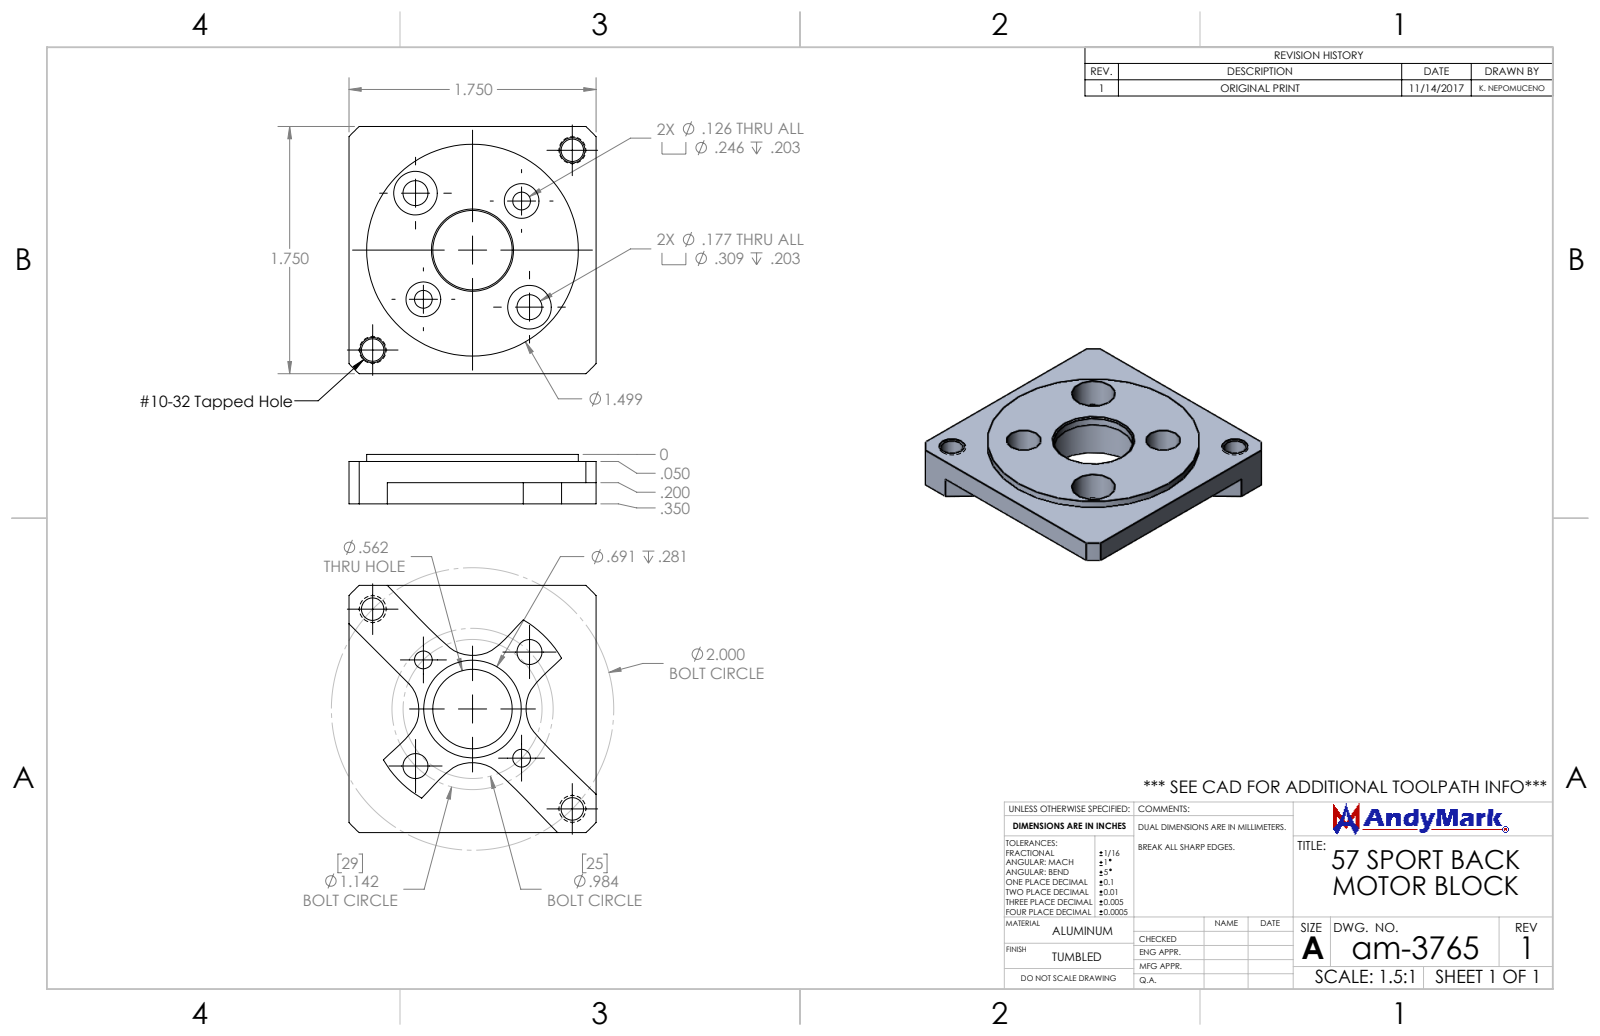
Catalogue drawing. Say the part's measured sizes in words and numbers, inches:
The part is named "am-3765 - 57 Sport Motor Block". Its 3-D file was written by "SolidWorks 2017 (CONFIG_CONTROL_DESIGN)". It is 1 solid with 57 faces: 15 planar, 32 cylindrical and 10 other. Overall it measures 1.75 by 1.75 by 0.35 inches. Its volume is 0.549 cubic inches and its surface area 9.665 square inches. Round holes: 2 of diameter 0.126, 2 of diameter 0.159, 2 of diameter 0.177, 2 of diameter 0.246, 2 of diameter 0.309, 1 of diameter 0.562, 1 of diameter 0.691. Round bosses or shafts: 1 of diameter 1.499. Partial cylindrical surfaces (rounded edges, fillets, slot ends): 1 of radius 0.726, 1 of radius 1.188. The main face-to-face distances are 0.15, 0.2, 0.05, 0.3, 0.35, 1.75, 1.75, 0.147, 0.153, 0.203. The hole center spacings are 0.754, 1.151, 0.492, 0.508, 0.571, 1, 1.492, 0.984.
